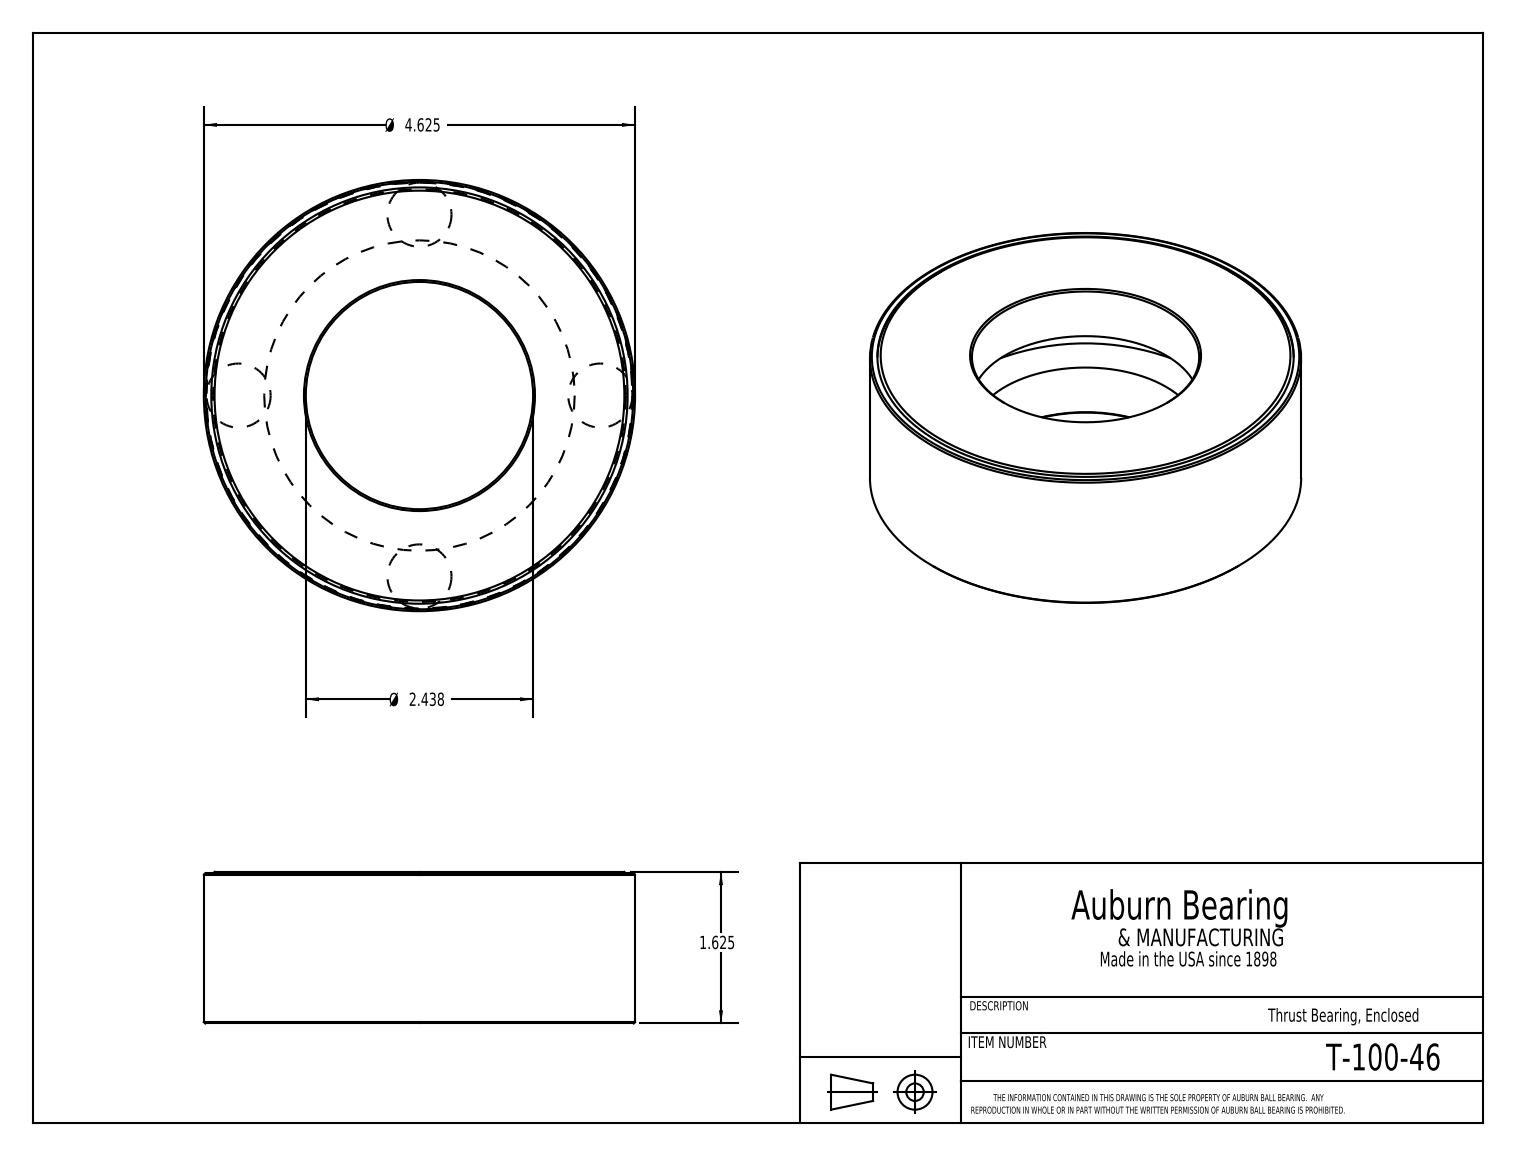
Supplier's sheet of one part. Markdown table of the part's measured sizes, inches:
| quantity | value |
| --- | --- |
| part name | T-100-46 |
| STEP written by | SolidWorks 2016 (CONFIG_CONTROL_DESIGN) |
| units | inches |
| bodies | 6 solids, 28 faces (9 planar, 7 cylindrical, 12 other) |
| overall size | 4.625 × 4.625 × 1.625 |
| volume | 14.11 in³ |
| surface area | 112.3 in² |
| round holes (diameter × count) | 2.437 × 1, 4.465 × 1, 4.585 × 1 |
| round bosses / shafts (diameter × count) | 4.625 × 1, 4.571 × 1 |
| main face-to-face distances | 1.625, 0.606, 1.019, 0.413, 1.59, 0.984, 0.571, 0.035, 1.61, 1.004 |
